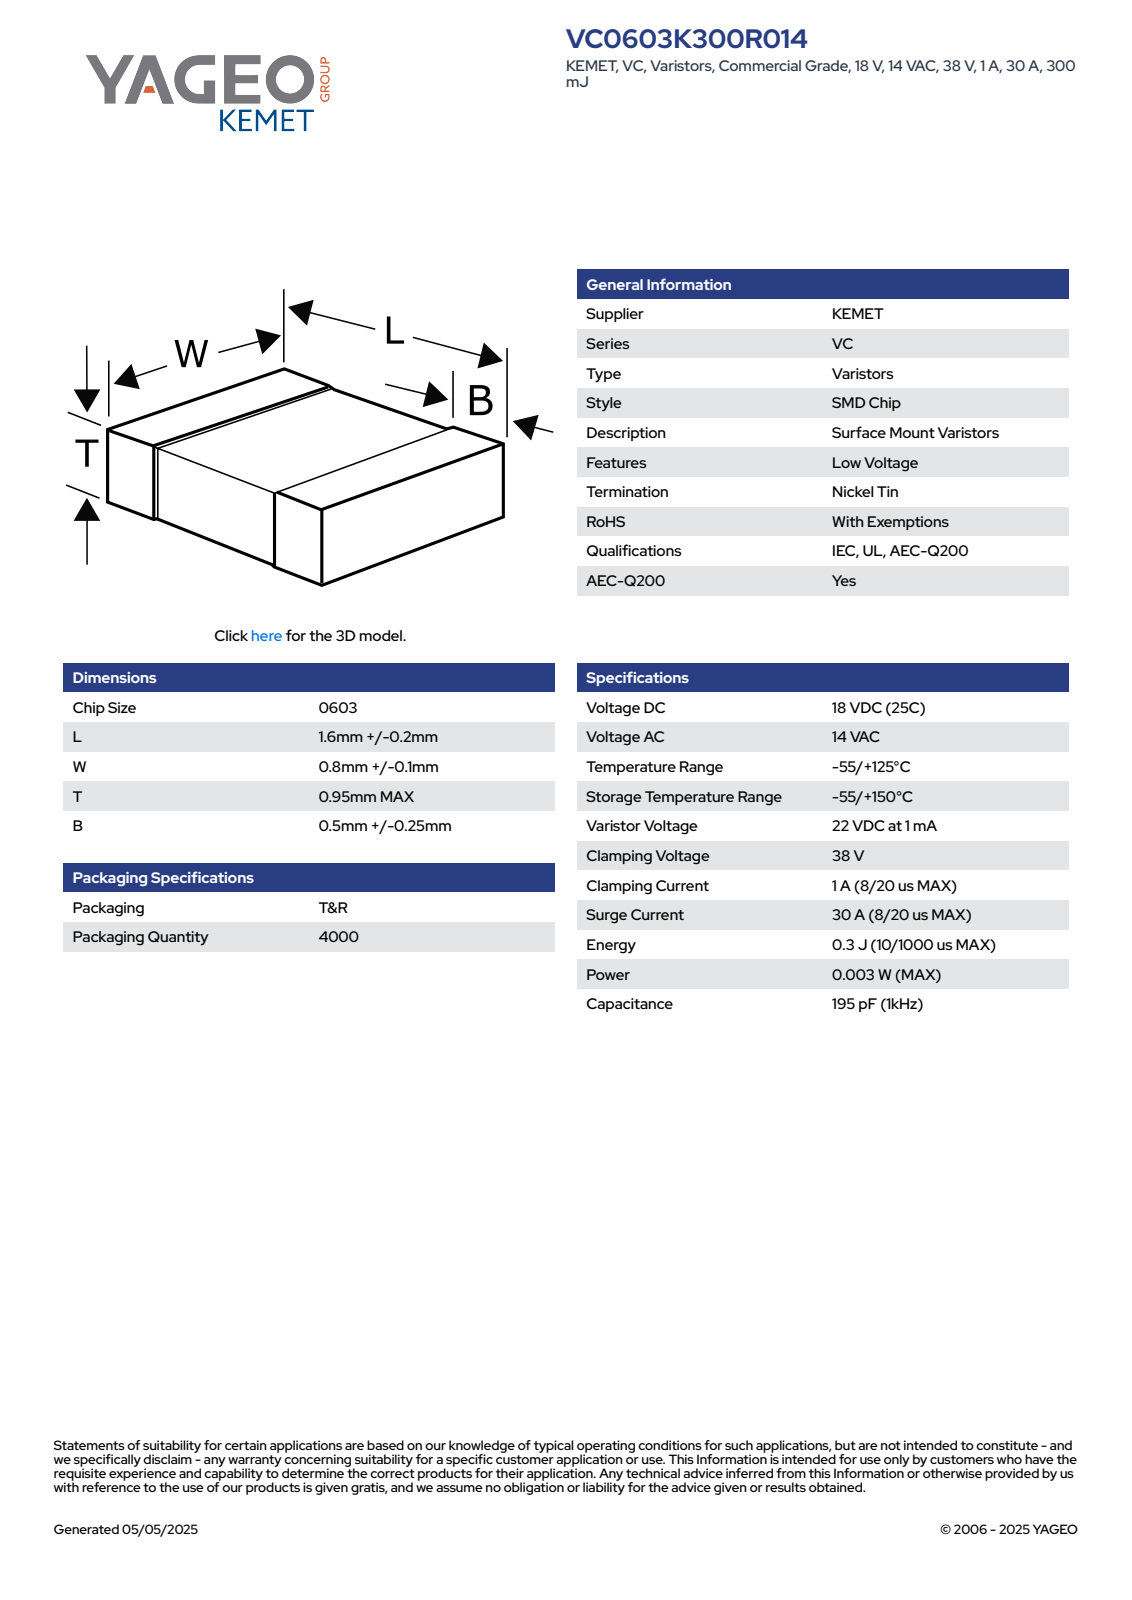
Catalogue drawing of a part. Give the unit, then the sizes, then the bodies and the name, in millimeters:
Units: millimetres
Overall size (bounding box): 1.8 × 0.95 × 0.9
Main face-to-face distances: 0.9, 0.95, 1.8, 0.93, 0.88, 0.86, 0.91, 0.94, 0.92, 0.84
Volume: 2 mm³ · Surface area: 8 mm²
Bodies: 4 solids, 121 faces (71 planar, 34 cylindrical, 16 other)
Part name (STEP PRODUCT): VS_SMD_0603_L1.80W0.9T0.95B0.75
STEP written by: SolidWorks 2014 (AUTOMOTIVE_DESIGN)
